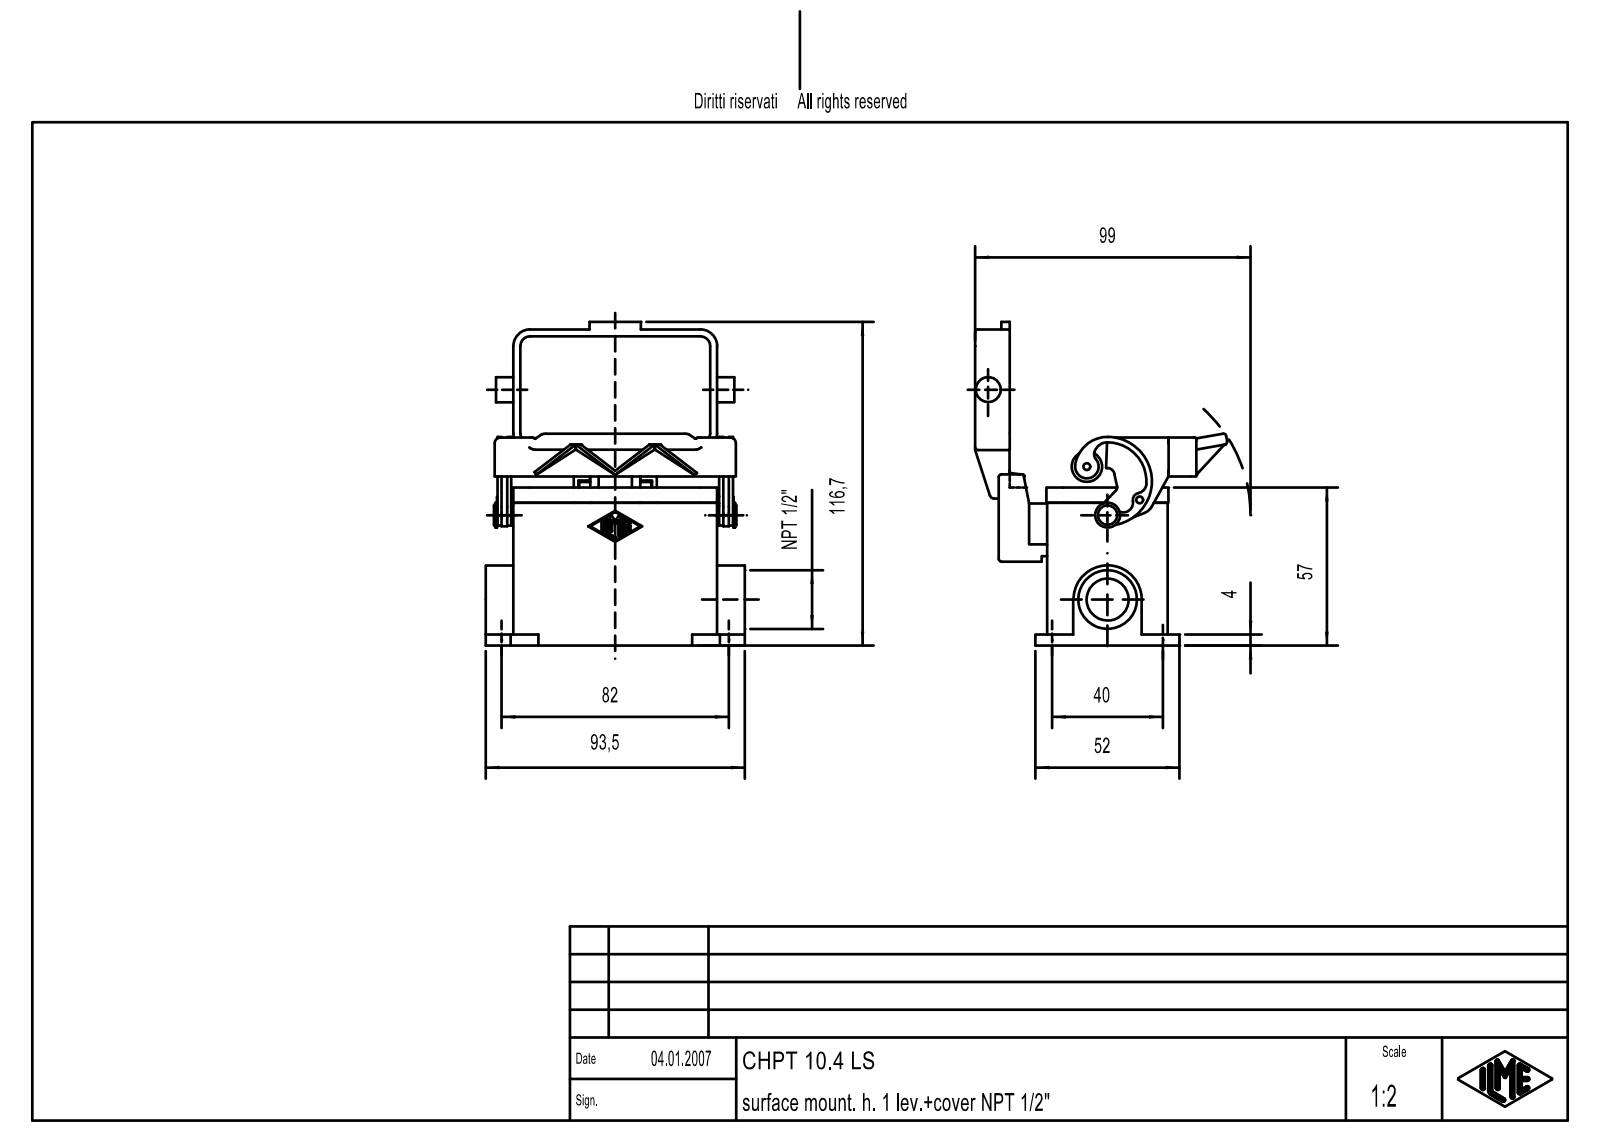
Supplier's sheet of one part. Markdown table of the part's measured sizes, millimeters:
| quantity | value |
| --- | --- |
| part name | MSBO10291; MSBO10291.1; MSBO111; MSBO459 (+2 more) |
| STEP written by | Creo Elements/Direct Modeling 18.0B 02-Dec-2011 (C) Parametric Technology GmbH (AUTOMOTIVE_DESIGN) |
| units | millimeters |
| bodies | 6 solids, 543 faces (286 planar, 197 cylindrical, 60 other) |
| overall size | 116.7 × 93.5 × 90.95 |
| volume | 113 608 mm³ |
| surface area | 63 767 mm² |
| round holes (diameter × count) | 2.46 × 4, 3 × 4, 5.5 × 4, 2 × 1, 4 × 1, 15.16 × 1, 21.16 × 1 |
| round bosses / shafts (diameter × count) | 9 × 2, 5 × 2, 11 × 1, 7 × 1, 4 × 1, 3 × 1, 2.5 × 1 |
| partial cylindrical surfaces (radius × count) | 1 × 18, 0.38 × 14, 2 × 12, 6 × 12, 1.5 × 6, 3.5 × 6, 3 × 4, 0.5 × 3 |
| main face-to-face distances | 3, 4, 40.5, 26, 43.5, 66, 66.5, 69.5, 25.5, 3.5 |
| hole center spacings | 14.09, 35.76, 69.8, 77.15, 27, 40, 57, 63.07 |
